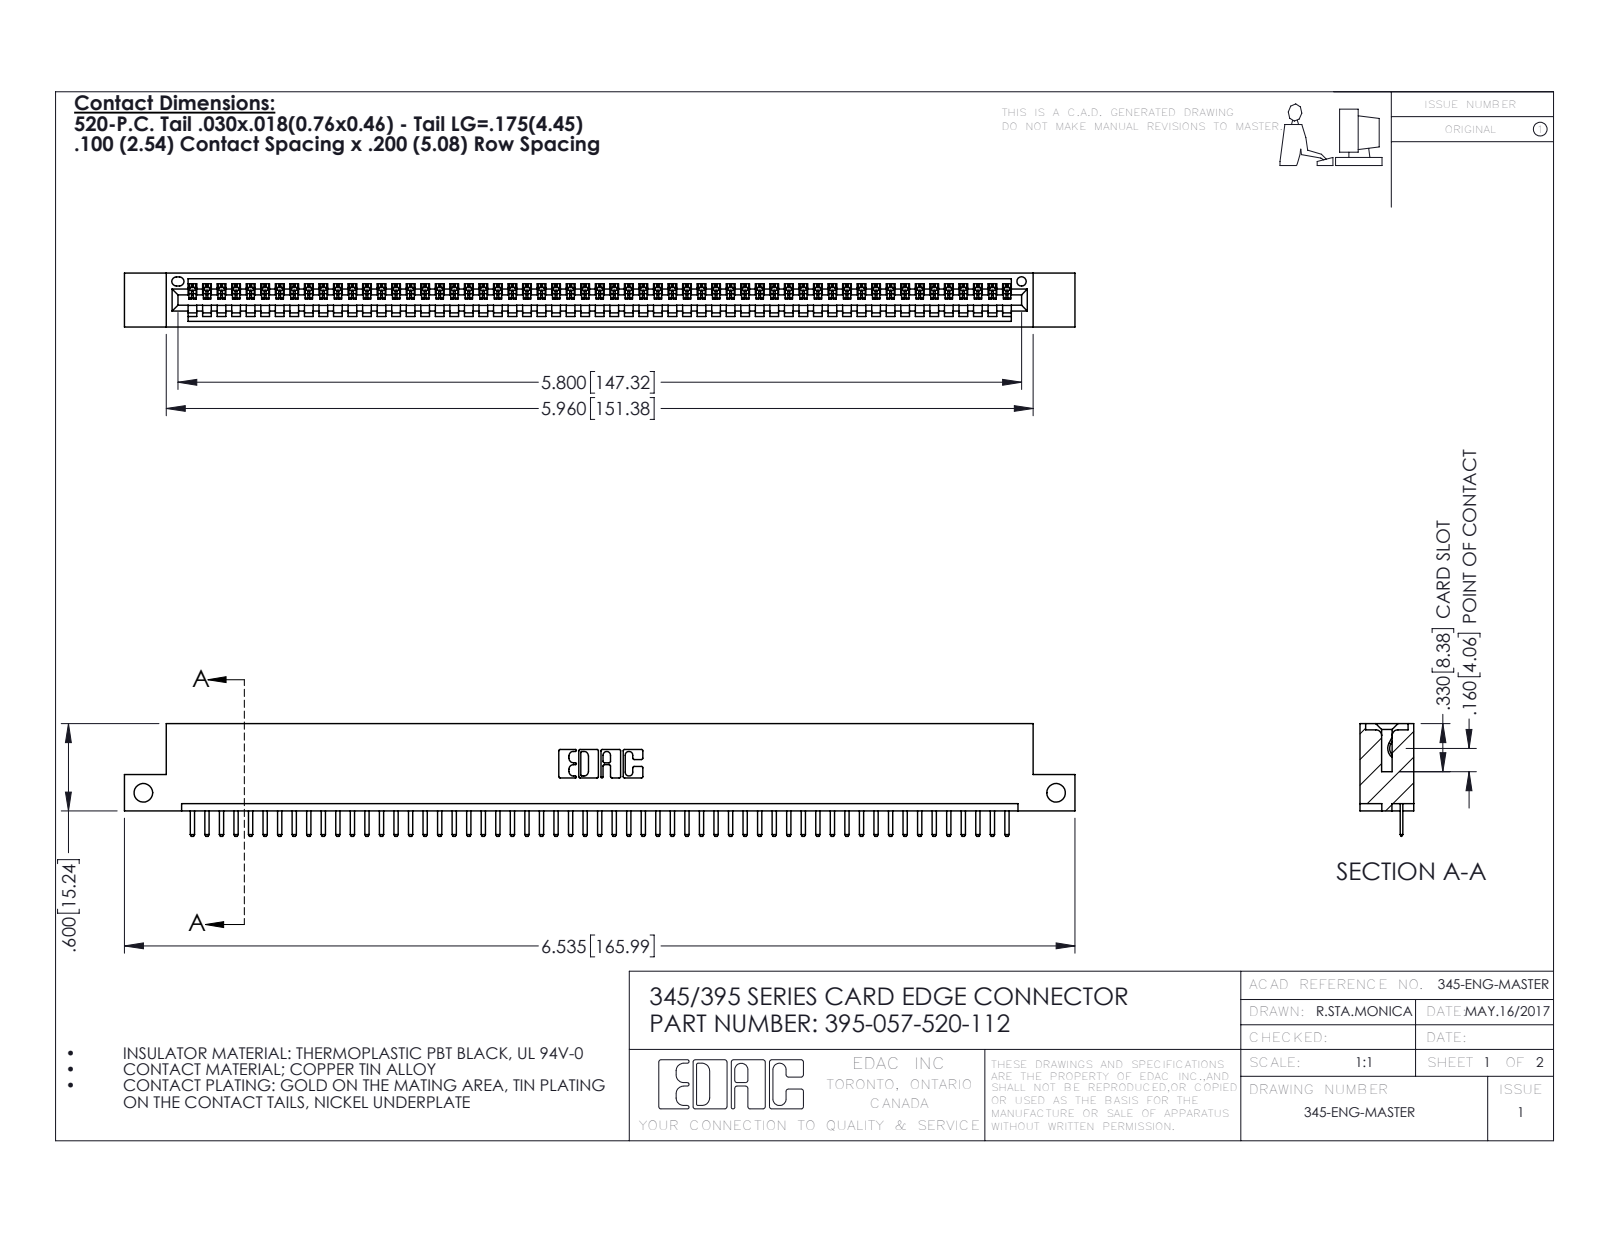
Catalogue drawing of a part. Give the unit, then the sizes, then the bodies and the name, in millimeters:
Units: millimetres
Overall size (bounding box): 166 × 19.7 × 9.4
Round holes (diameter × count): ⌀3.3 ×2, ⌀1.6 ×1
Partial cylindrical surfaces — rounded edges, fillets, slot ends (radius × count): R0.3 ×116, R0.2 ×114, R0.3 ×22, R0.2 ×6, R0.8 ×6, R0.7 ×3, R0.8 ×2, R1 ×2
Main face-to-face distances: 7.6, 1.8, 9.4, 5.1, 2.5, 6.9, 0.6, 5.7, 1.8, 3.8
Hole centre spacings: 159.4
Volume: 15 600 mm³ · Surface area: 20 300 mm²
Bodies: 58 solids, 3660 faces (2474 planar, 1186 cylindrical, 0 other)
Part name (STEP PRODUCT): 345-292-001_345-293-120; 395-057-520-112; 345 Part_Flush Mounting Lugs - Side Mount
STEP written by: SolidWorks 2016 (CONFIG_CONTROL_DESIGN)
